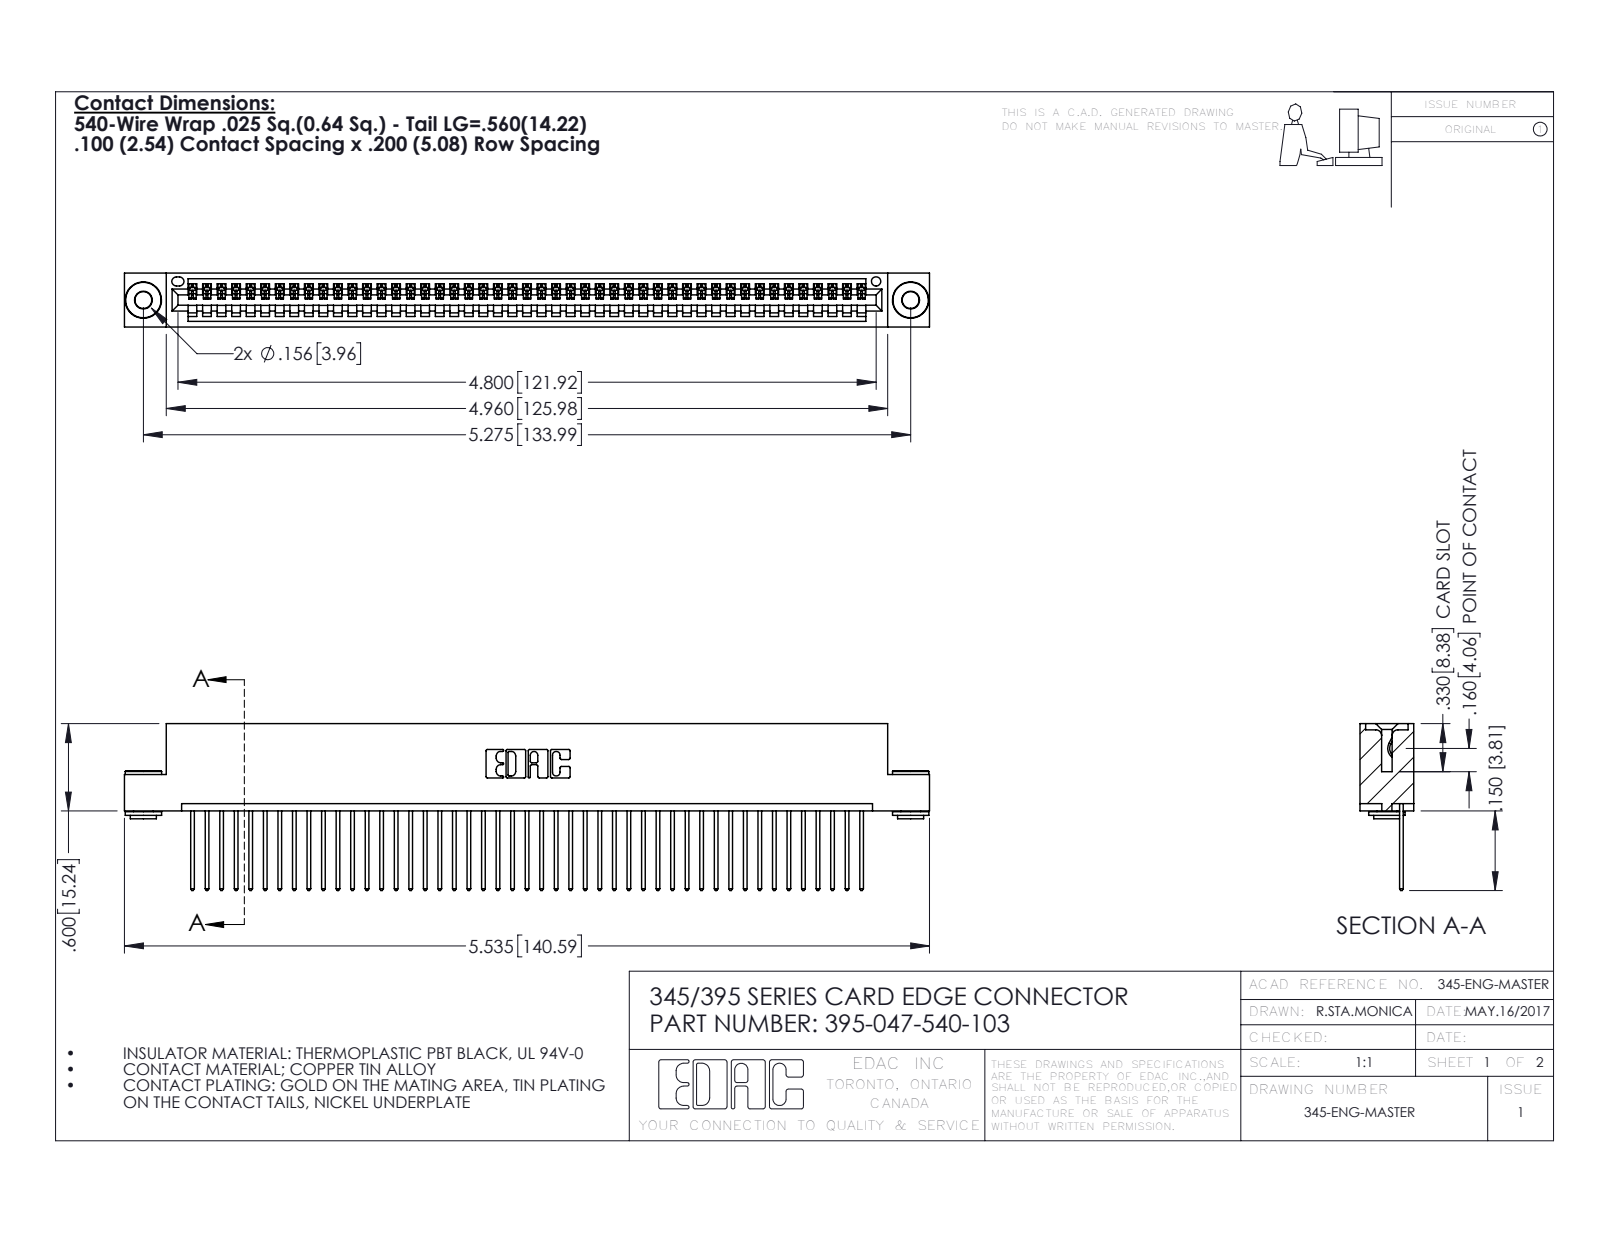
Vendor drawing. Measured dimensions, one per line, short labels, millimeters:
name: 345-292-001_345-293-140; 345-250-002_345-250-002-102; 345 Part_Flush Mounting Lugs - 0.156 Dia-TH; 395-047-540-103
written by: SolidWorks 2016 (CONFIG_CONTROL_DESIGN)
unit: mm
bodies: 50 solids, 2890 faces (1970 planar, 912 cylindrical, 8 other)
size: 140.6 × 29.1 × 9.4
volume: 13 500 mm³; area: 18 650 mm²
holes: 2× ⌀2.9, 2× ⌀4, 1× ⌀1.6
bosses: 2× ⌀6.4, 2× ⌀4.6, 2× ⌀3.5
rounds: 94× R0.2, 94× R0.3, 22× R0.3, 6× R0.2, 6× R0.8, 3× R0.7, 2× R0.8, 2× R1
face distances: 1.8, 7.6, 5.1, 9.4, 0.6, 2.5, 6.9, 5.7, 3.8, 1.8
hole spacings: 6.9, 128, 134
